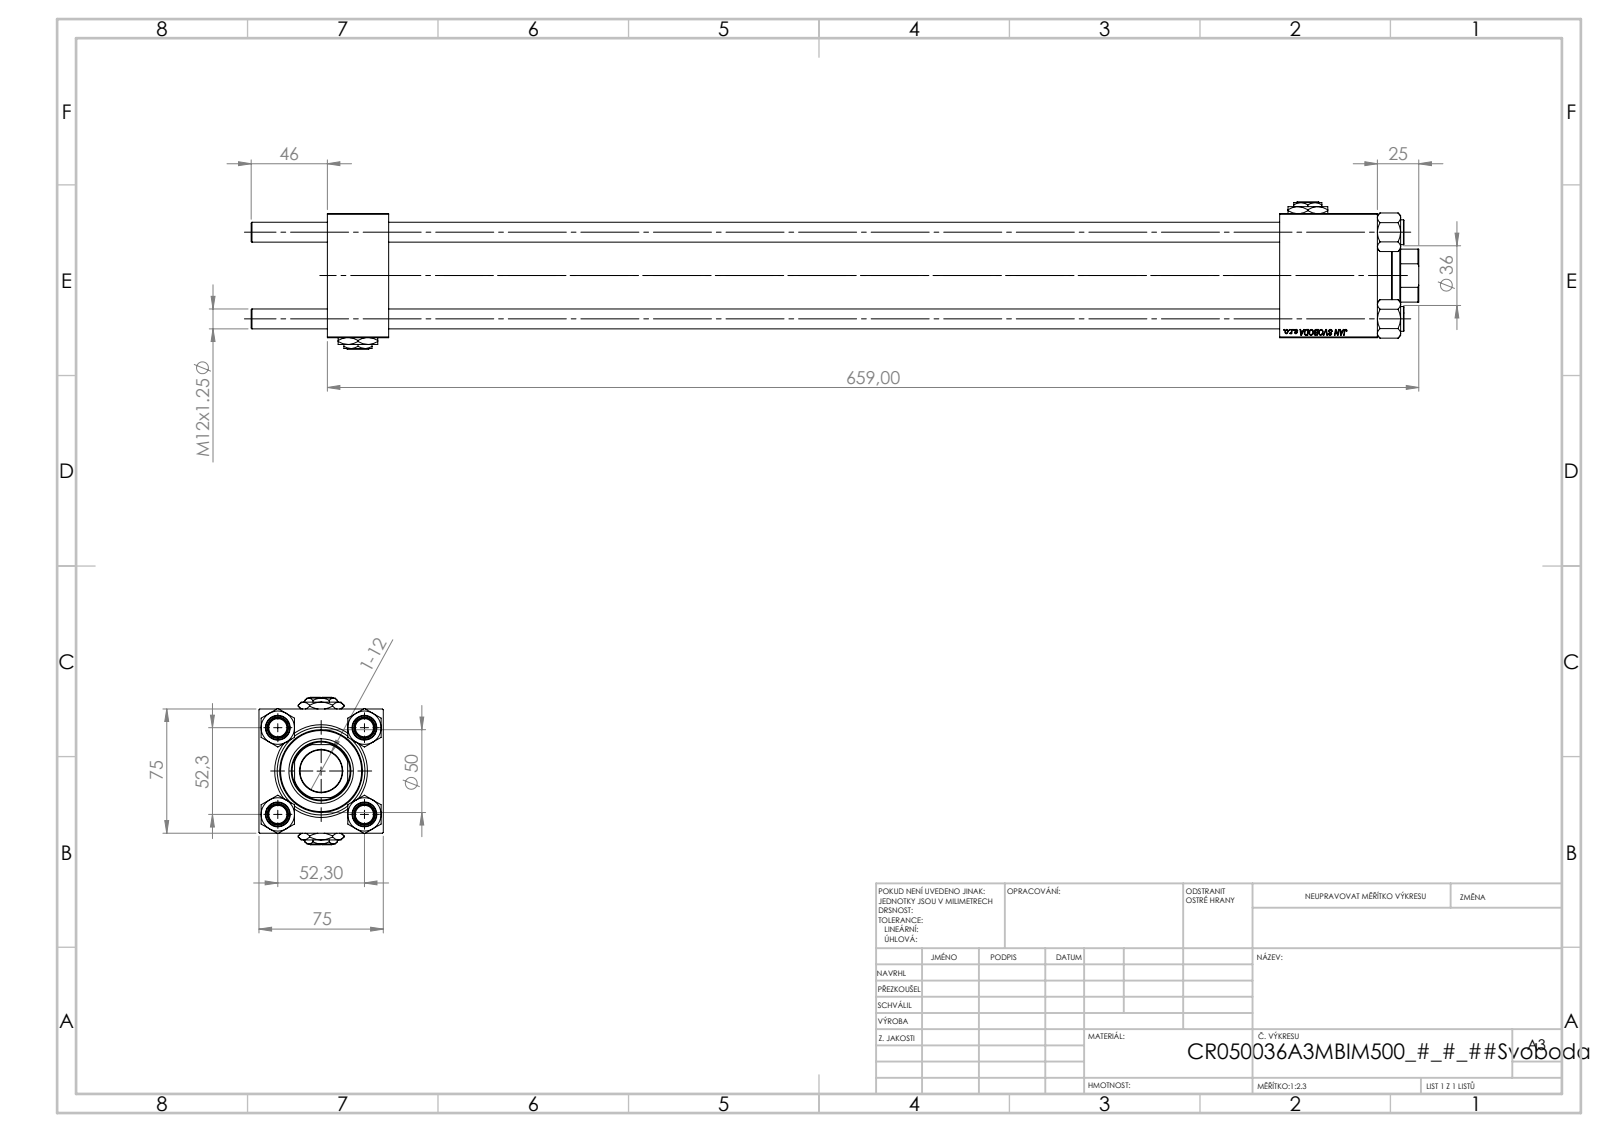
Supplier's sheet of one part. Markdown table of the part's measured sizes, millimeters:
| quantity | value |
| --- | --- |
| part name | CR025_012_A_0_G_A_G_M_020_+#_##_TYCINKA; V215CR_VCP; V215_VC_A; Zatka_pro_OIL_PORT (+2 more) |
| STEP written by | SolidWorks 2019 (CONFIG_CONTROL_DESIGN) |
| units | millimeters |
| bodies | 13 solids, 1233 faces (567 planar, 88 cylindrical, 578 other) |
| overall size | 705 × 89 × 75 |
| volume | 1 660 000 mm³ |
| surface area | 462 937 mm² |
| round holes (diameter × count) | 12 × 4, 7 × 2, 20.96 × 2, 30 × 2, 25.5 × 1, 36 × 1, 39 × 1, 41 × 1, 53 × 1 |
| round bosses / shafts (diameter × count) | 15 × 4, 56 × 1, 50 × 1 |
| partial cylindrical surfaces (radius × count) | 17.5 × 1 |
| main face-to-face distances | 75, 37, 575, 634, 597, 59, 538, 74.8, 605.3, 568.3 |
| hole center spacings | 36.98, 52.3, 73.96, 573.5 |
